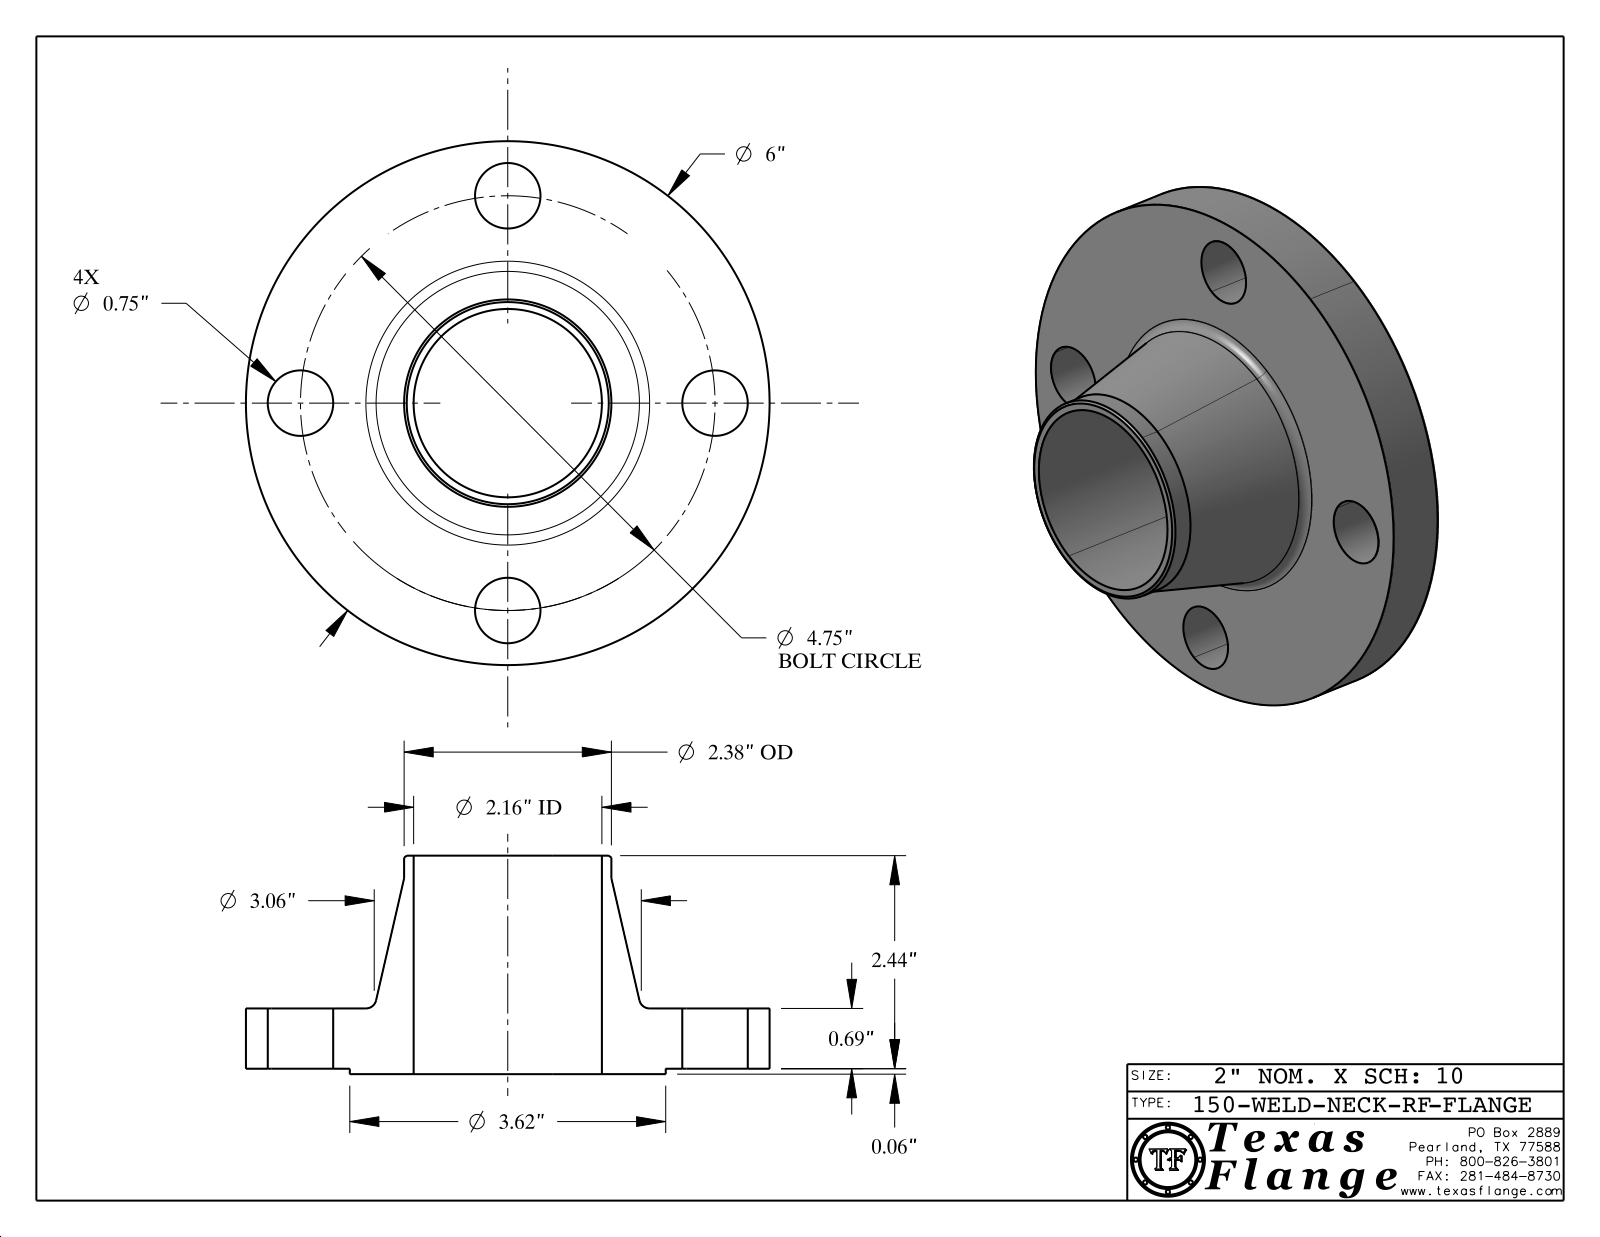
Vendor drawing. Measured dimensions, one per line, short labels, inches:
name: 150-WELD-NECK-RF
written by: CATIA V5 STEP AP214 (AUTOMOTIVE_DESIGN)
unit: in
bodies: 1 solid, 411 faces (369 planar, 36 cylindrical, 6 other)
size: 6 × 6 × 2.503
volume: 19.64 in³; area: 94.65 in²
holes: 4× ⌀0.75, 1× ⌀0.495, 1× ⌀2.157
bosses: 8× ⌀0.03, 1× ⌀6, 1× ⌀3.62, 1× ⌀2.375, 1× ⌀0.39
face distances: 0.69, 0.063, 0.753, 2.503, 2.44, 1.75, 0.738, 0.675, 0.015, 1.765
hole spacings: 2.375, 3.359, 1.818, 4.389, 4.75
